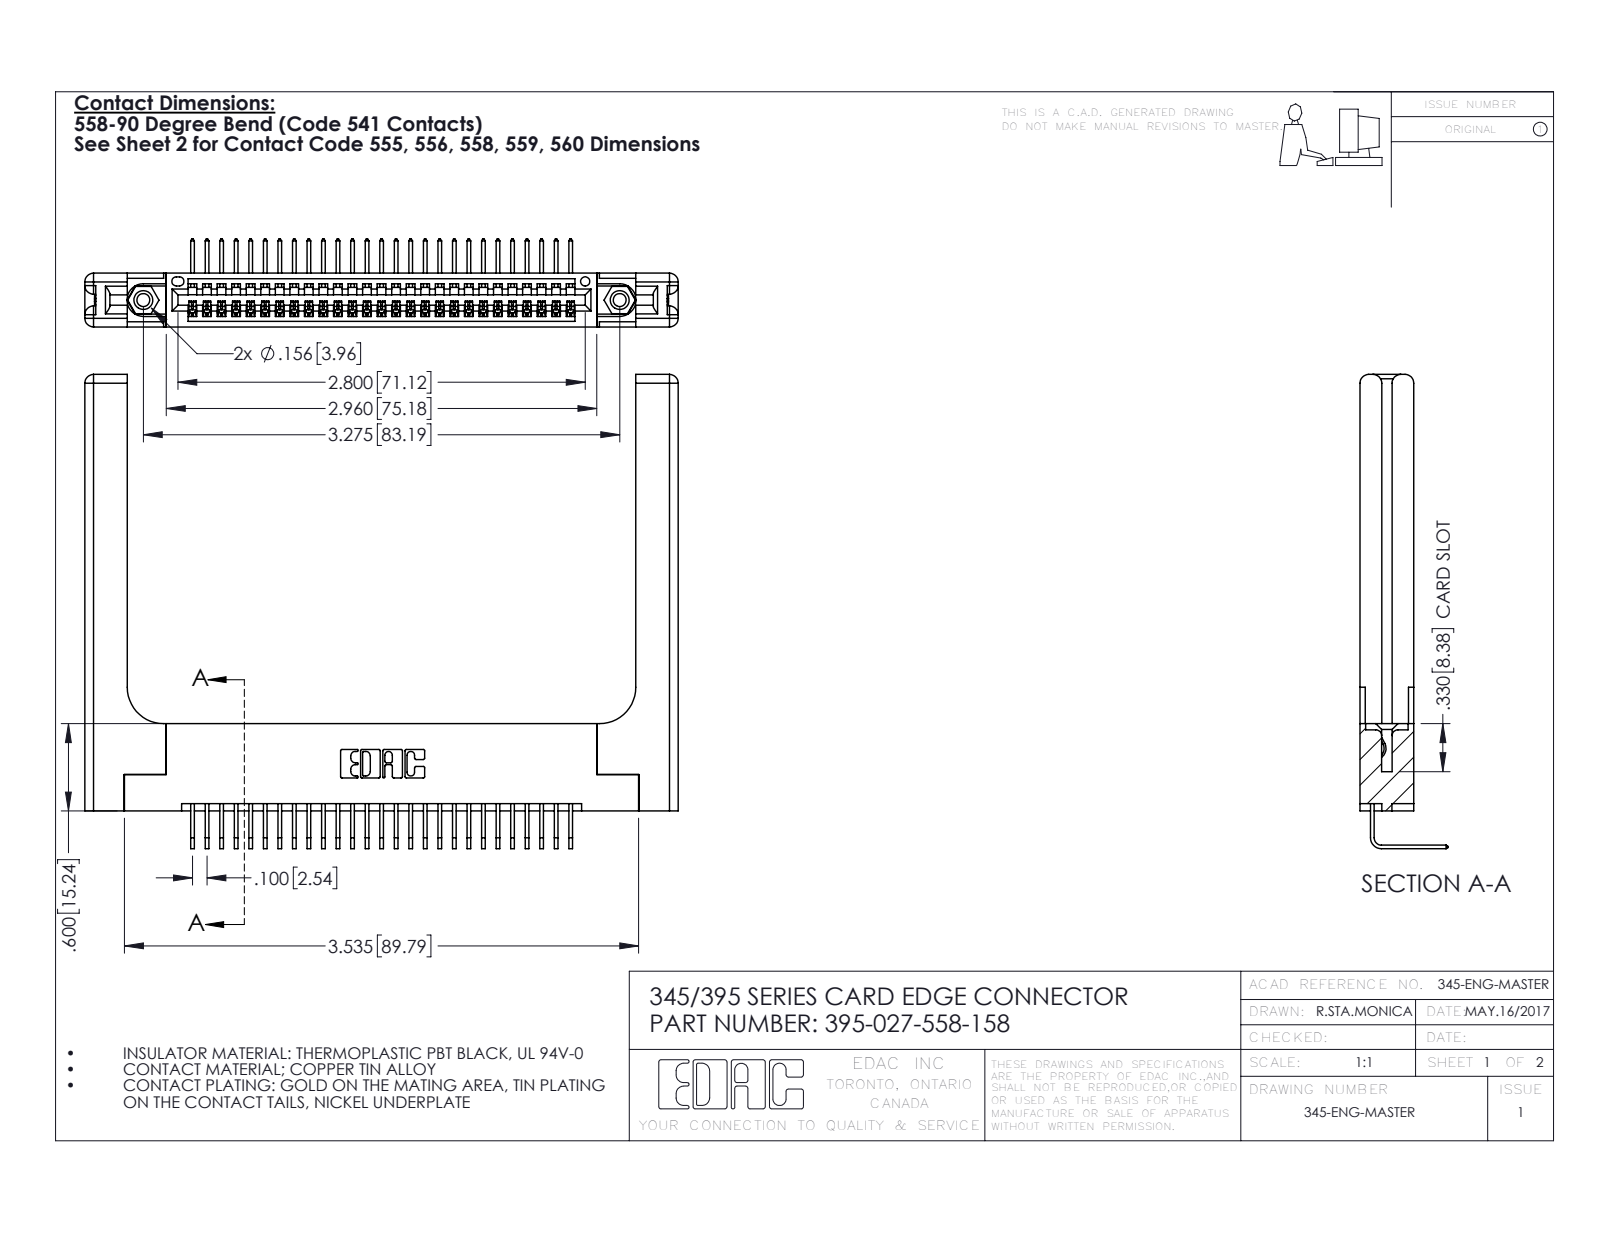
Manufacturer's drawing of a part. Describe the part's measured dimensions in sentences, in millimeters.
The part is named "345-250-001_345-250-001-102; 345-292-001_558 Tail - 2; 345 Part_Flush Mounting Lugs - 0.156 Dia-TH; 345-220-058_345-220-058 (+1 more)". Its 3-D file was written by "SolidWorks 2016 (CONFIG_CONTROL_DESIGN)". It is 32 solids with 2002 faces: 1362 planar, 580 cylindrical and 60 other. Overall it measures 103.6 by 82.8 by 15.4 millimeters. Its volume is 18 320 cubic millimeters and its surface area 18 660 square millimeters. Round holes: 2 of diameter 2.3, 2 of diameter 3.2, 2 of diameter 4, 1 of diameter 1.6. Round bosses or shafts: 2 of diameter 3.9. Partial cylindrical surfaces (rounded edges, fillets, slot ends): 54 of radius 0.2, 22 of radius 0.3, 16 of radius 1.5, 6 of radius 0.2, 6 of radius 0.8, 3 of radius 0.7, 2 of radius 0.8, 2 of radius 0.8. The main face-to-face distances are 9.4, 1.8, 7.6, 5.1, 3.8, 3.8, 2.5, 6.9, 0.6, 2. The hole center spacings are 6.9, 77.2, 83.2.
